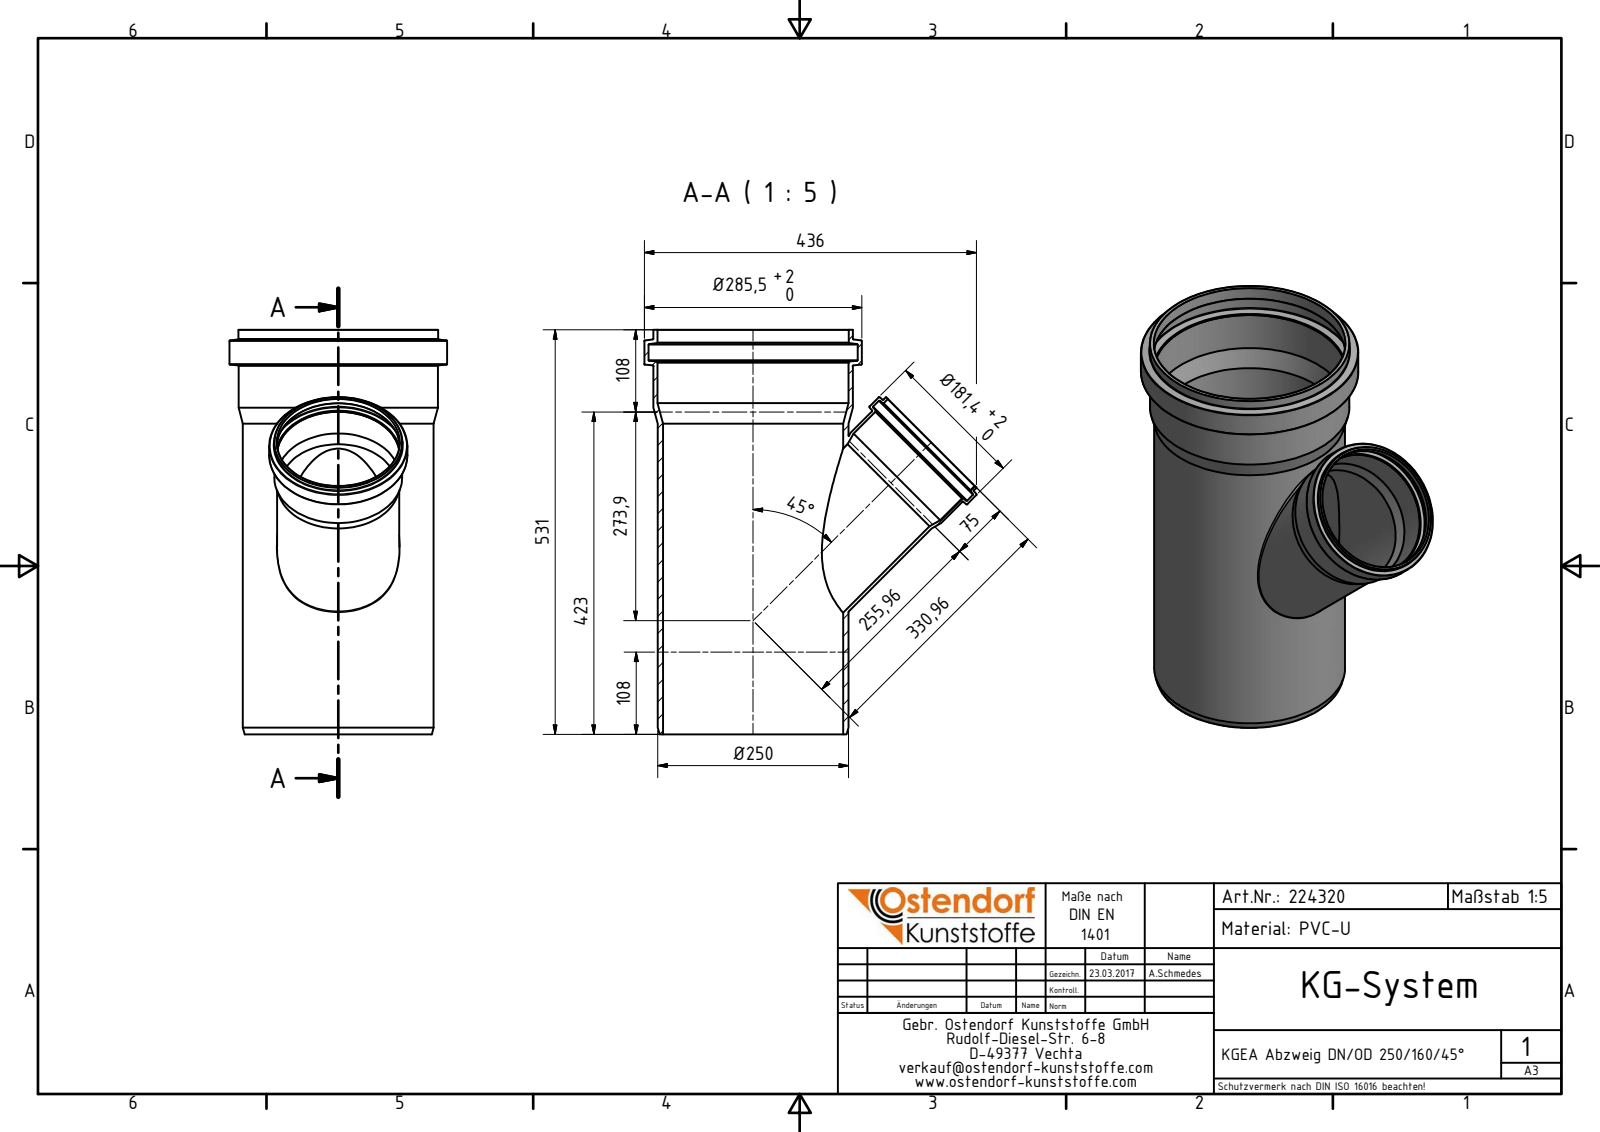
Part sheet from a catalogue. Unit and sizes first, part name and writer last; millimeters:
Units: millimetres
Overall size (bounding box): 531 × 436.11 × 285.5
Round holes (diameter × count): ⌀161.1 ×2, ⌀152.3 ×1, ⌀160.7 ×1, ⌀174.4 ×1, ⌀236.3 ×1, ⌀250.8 ×1, ⌀251.1 ×1, ⌀274.5 ×1
Round bosses / shafts (diameter × count): ⌀285.5 ×1, ⌀262.1 ×1, ⌀261.8 ×1, ⌀250.5 ×1, ⌀181.4 ×1, ⌀168.1 ×1, ⌀167.7 ×1, ⌀160.3 ×1
Main face-to-face distances: 531, 487.77, 43.23, 23.6
Volume: 3 049 000 mm³ · Surface area: 1 003 000 mm²
Bodies: 1 solid, 57 faces (5 planar, 18 cylindrical, 34 other)
Part name (STEP PRODUCT): 224320 KGEA Abzweig DN_OD 250_160_45°
STEP written by: Autodesk Inventor 2016 (AUTOMOTIVE_DESIGN)
